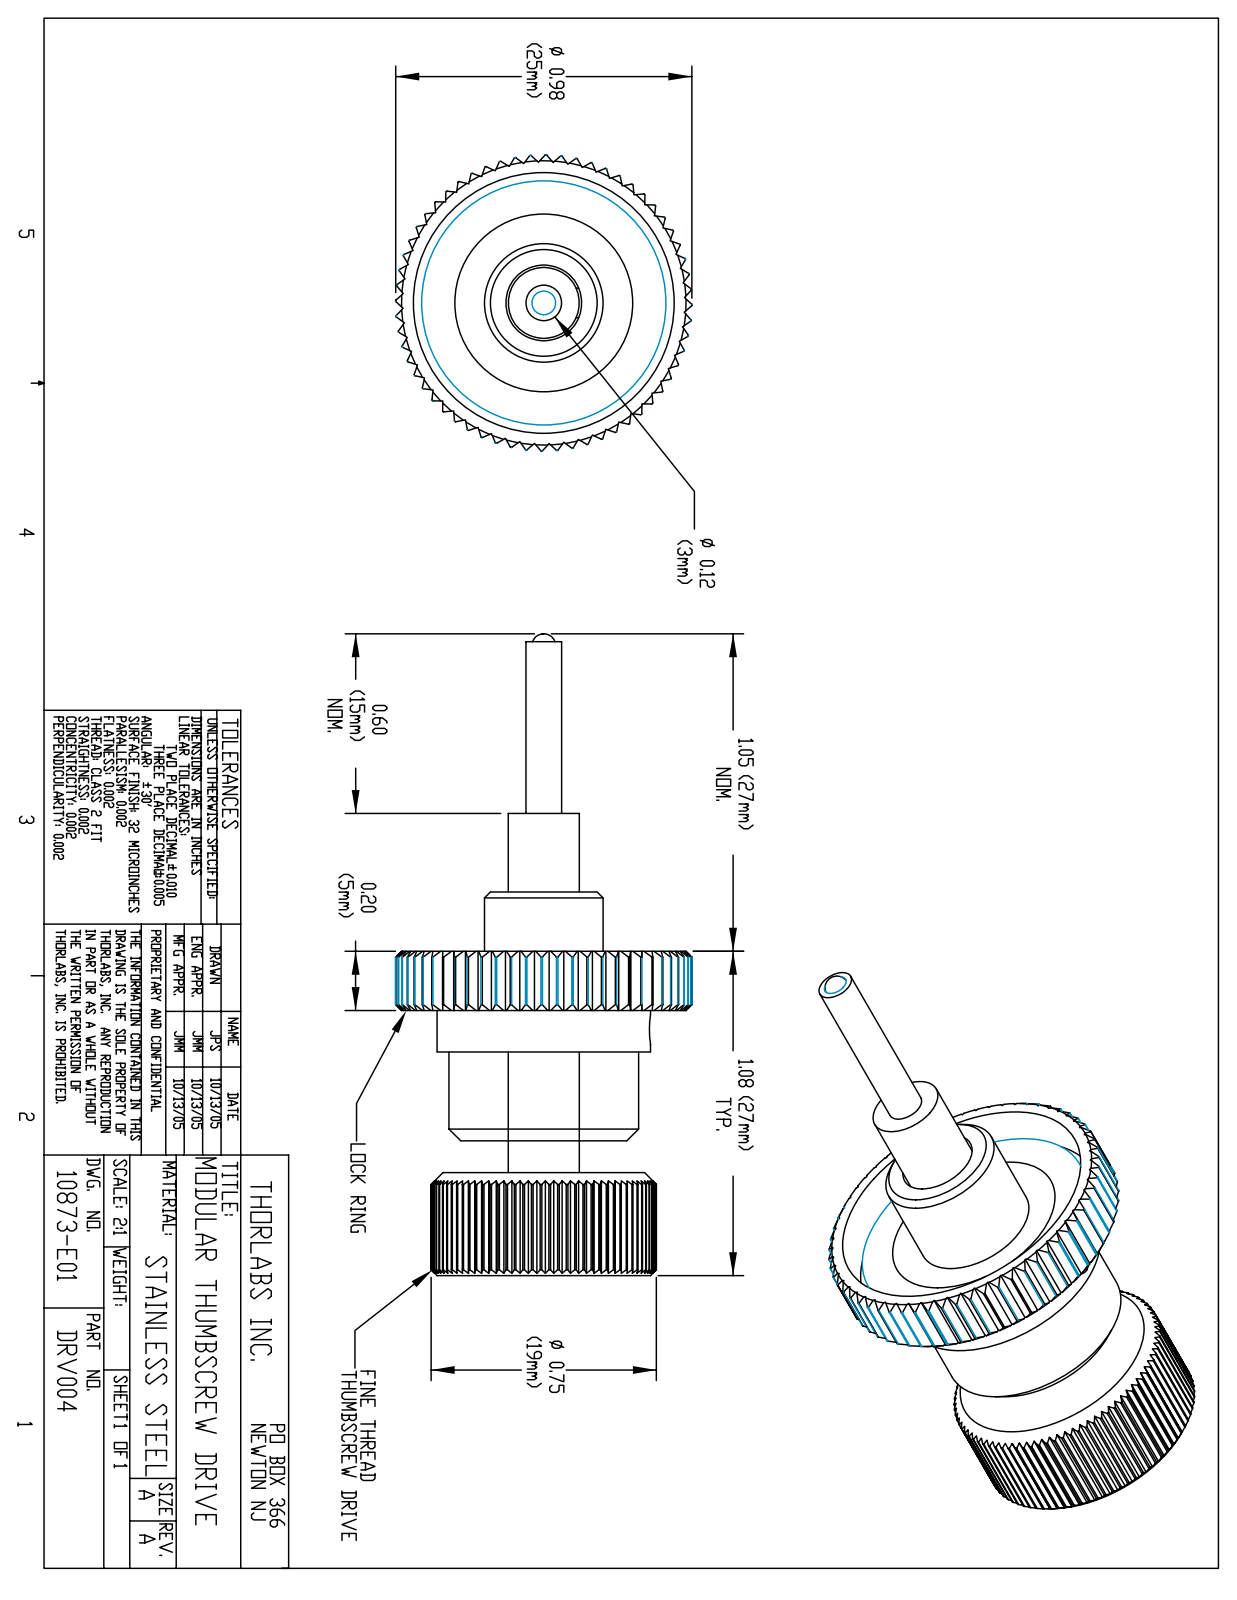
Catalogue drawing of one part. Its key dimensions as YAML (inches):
part_name: "10873-E0W"
step_written_by: "SolidWorks 2007 (AUTOMOTIVE_DESIGN)"
units: inches
bodies: {solids: 0, faces: 636, planar: 342, cylindrical: 162, other: 132}
overall_size: [2.133, 0.984, 0.984]
round_holes:
  - {diameter: 0.098, count: 1}
  - {diameter: 0.252, count: 1}
  - {diameter: 0.681, count: 1}
  - {diameter: 0.724, count: 1}
  - {diameter: 0.866, count: 1}
round_bosses_or_shafts:
  - {diameter: 0.709, count: 1}
  - {diameter: 0.63, count: 1}
  - {diameter: 0.394, count: 1}
  - {diameter: 0.236, count: 1}
  - {diameter: 0.118, count: 1}
partial_cylinders:
  - {radius: 0.374, count: 1}
  - {radius: 0.492, count: 1}
face_to_face_distances: [0.335, 0.098, 0.924, 0.589, 0.873, 0.538, 0.051, 0.531, 0.971, 0.637]
